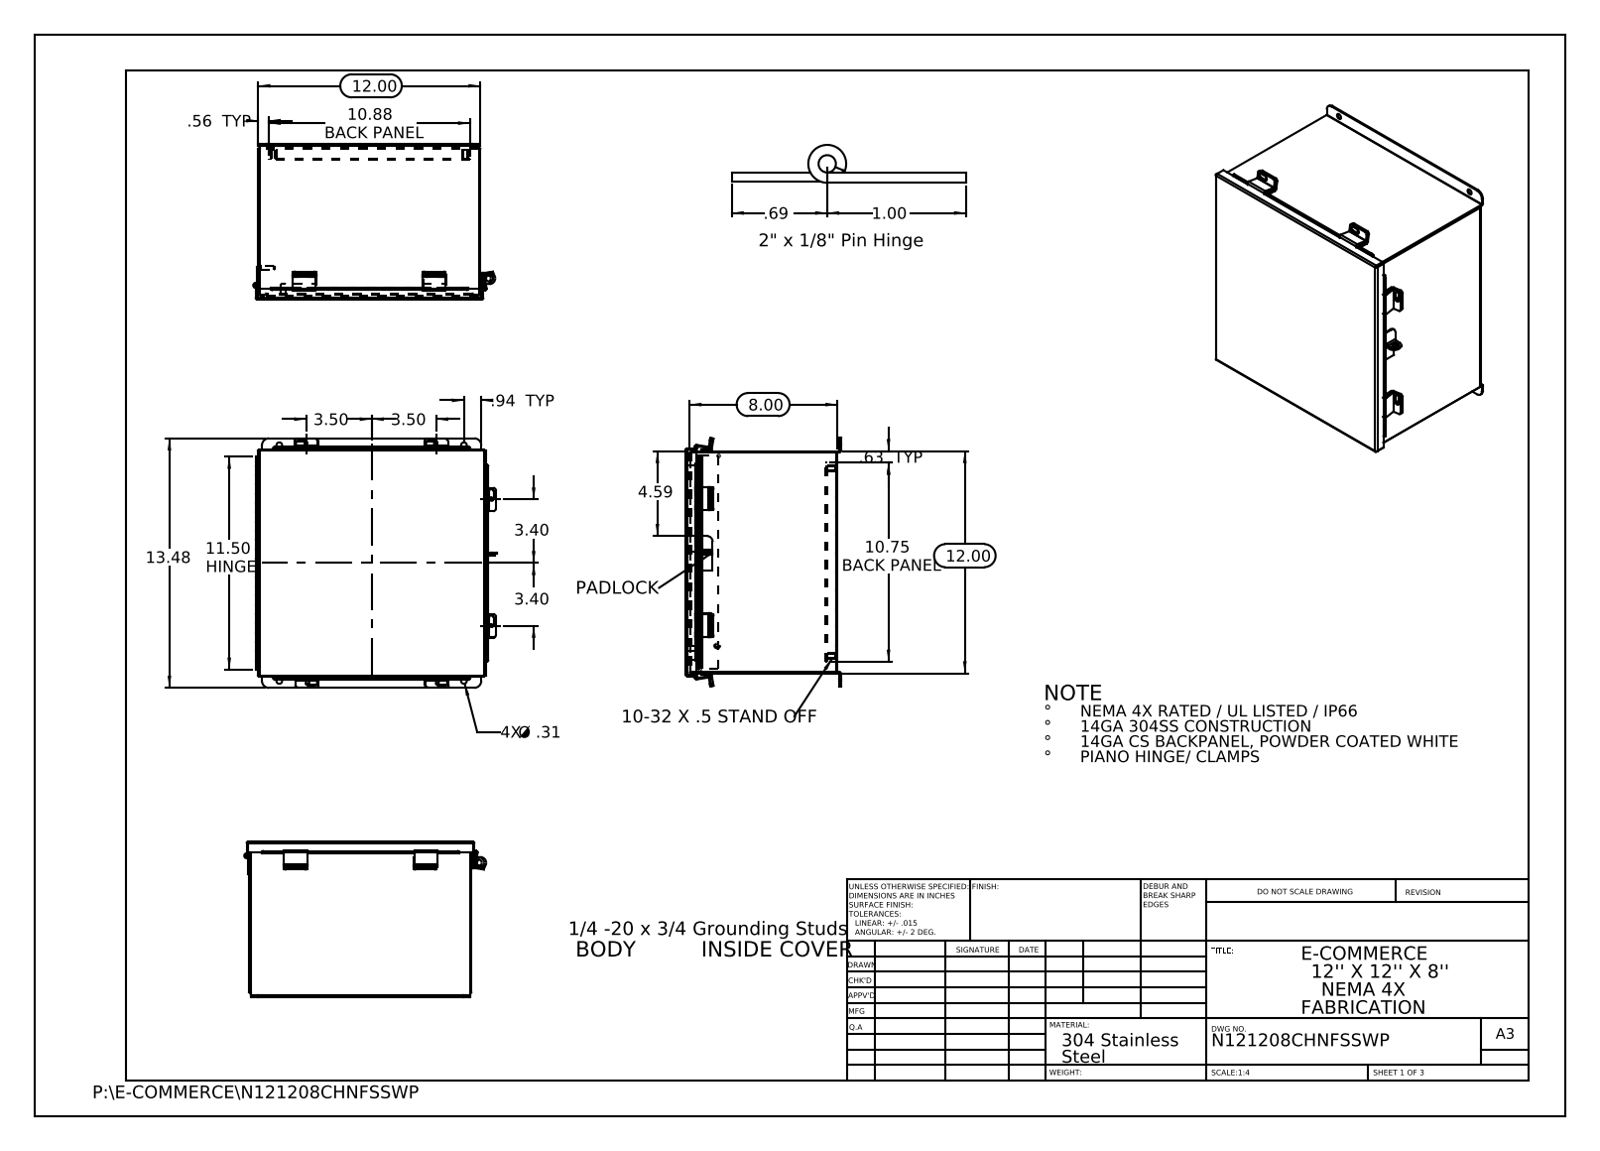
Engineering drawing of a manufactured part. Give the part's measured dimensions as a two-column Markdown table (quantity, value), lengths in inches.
| quantity | value |
| --- | --- |
| part name | N121208CHNFSSWP JIC Backpanel; N121208CHNFSSWP Hinge Body Side; N121208CHNFSSWP JIC Cover Clamp; N121208CHNFSSWP (+8 more) |
| STEP written by | SolidWorks 2013 (CONFIG_CONTROL_DESIGN) |
| units | inches |
| bodies | 27 solids, 794 faces (499 planar, 275 cylindrical, 20 other) |
| overall size | 13.476 × 13.072 × 8.39 |
| volume | 66.97 in³ |
| surface area | 1 824 in² |
| round holes (diameter × count) | 0.25 × 10, 0.187 × 4, 0.312 × 4, 0.125 × 1, 0.125 × 1, 0.373 × 1, 0.375 × 1 |
| round bosses / shafts (diameter × count) | 0.313 × 4, 0.315 × 2, 0.236 × 2, 0.273 × 1, 0.25 × 1 |
| partial cylindrical surfaces (radius × count) | 0.125 × 21, 0.013 × 13, 0.009 × 12, 0.088 × 12, 0.133 × 12, 0.083 × 6, 0.1 × 6, 0.375 × 4 |
| main face-to-face distances | 0.075, 11.925, 8.128, 11.85, 12, 8.053, 8.203, 0.074, 0.575, 0.5 |
| hole center spacings | 1.315, 10.258, 11.428, 15.3, 7, 9.976, 10.126, 10.375 |
